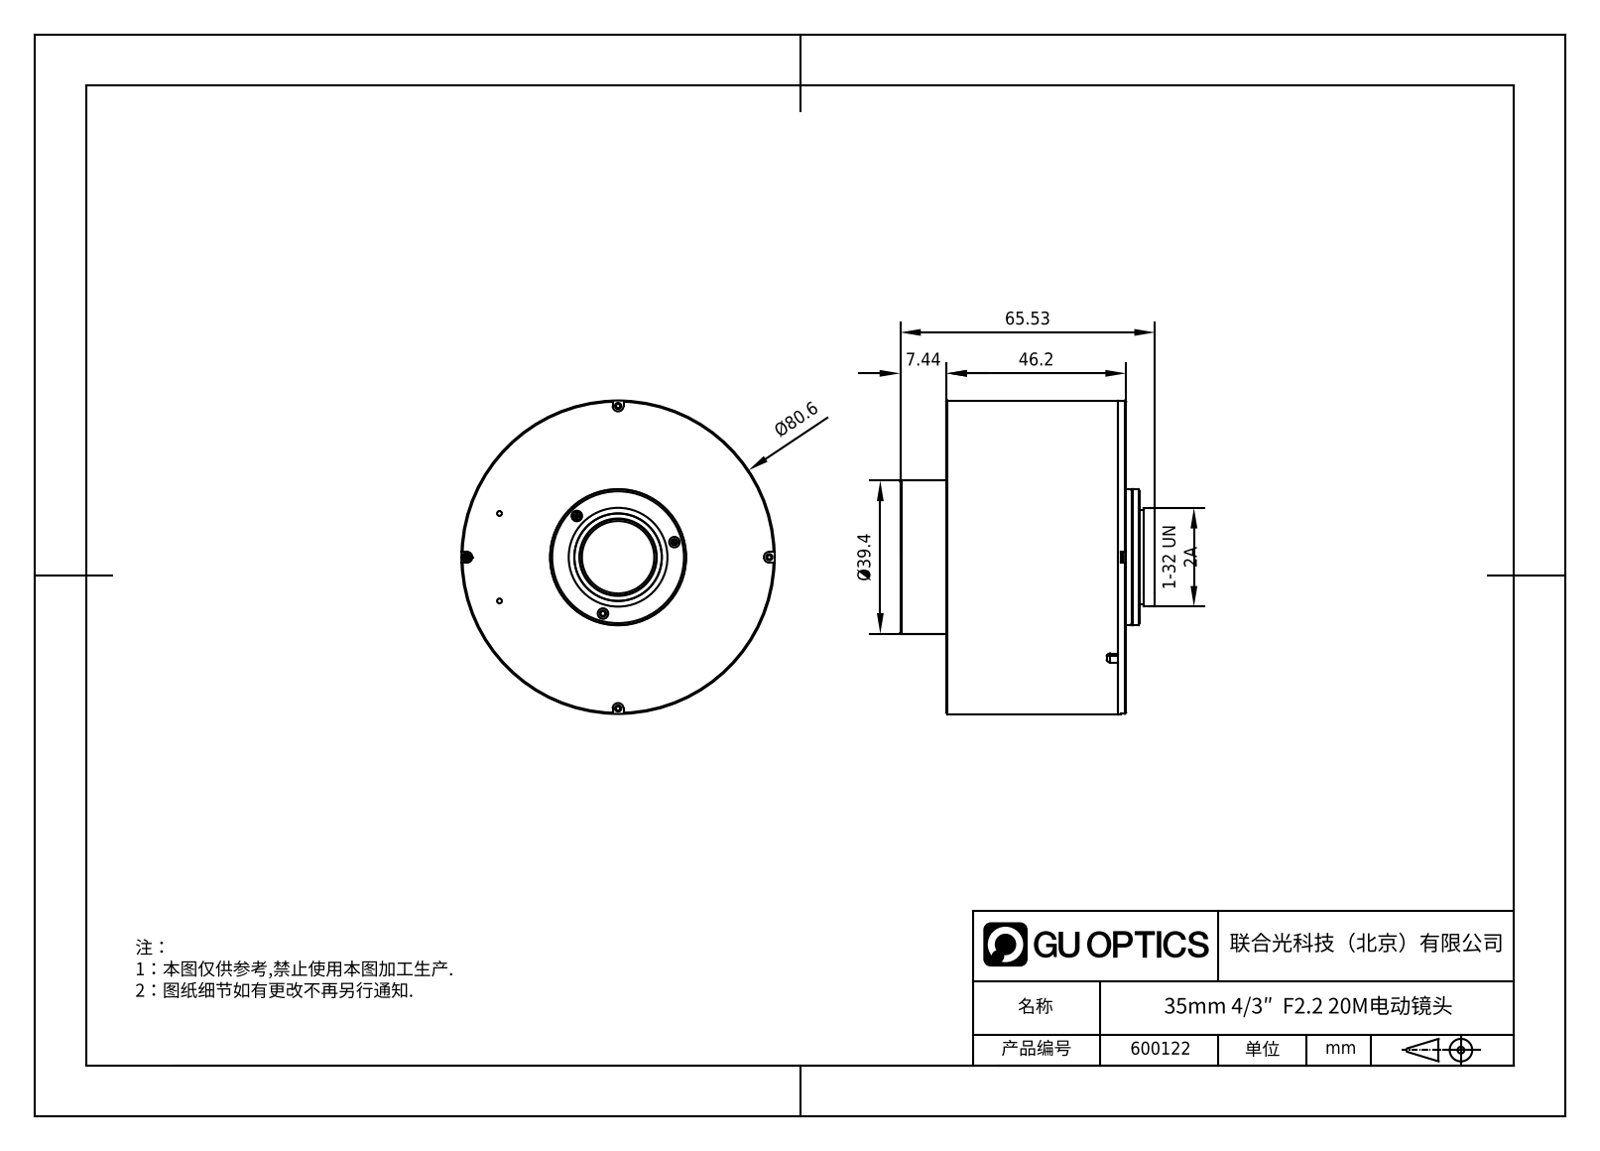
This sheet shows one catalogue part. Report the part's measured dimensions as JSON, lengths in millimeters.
{"part_name": "600122", "step_written_by": "SolidWorks 2020 (CONFIG_CONTROL_DESIGN)", "units": "millimeters", "bodies": {"solids": 65, "faces": 1451, "planar": 660, "cylindrical": 693, "other": 98}, "overall_size": [80.6, 80.6, 65.53], "volume_mm3": 69228, "surface_area_mm2": 87172, "round_holes": [[1.6, 26], [1.25, 20], [1.1, 14], [1.9, 13], [2.2, 7], [2.7, 7], [1.3, 4], [1.8, 4], [2.1, 4], [2.8, 3], [4, 3], [3, 2]], "round_bosses_or_shafts": [[2.5, 18], [1.7, 14], [1, 10], [2.8, 8], [2, 8], [1.4, 8], [3.45, 4], [2.7, 4]], "partial_cylinders_radius": [[9.6, 121], [1.2, 48], [1, 30], [2.5, 8], [1.25, 6], [1.05, 4], [1.4, 4], [21.4, 3]], "face_to_face_distances": [1.2, 46.2, 45, 1.5, 1.3, 44.9, 43.7, 2, 9.78, 0.5], "hole_center_spacings": [42.74, 28.02, 15, 27.37, 38.9, 7.5, 17.7, 21.2]}
